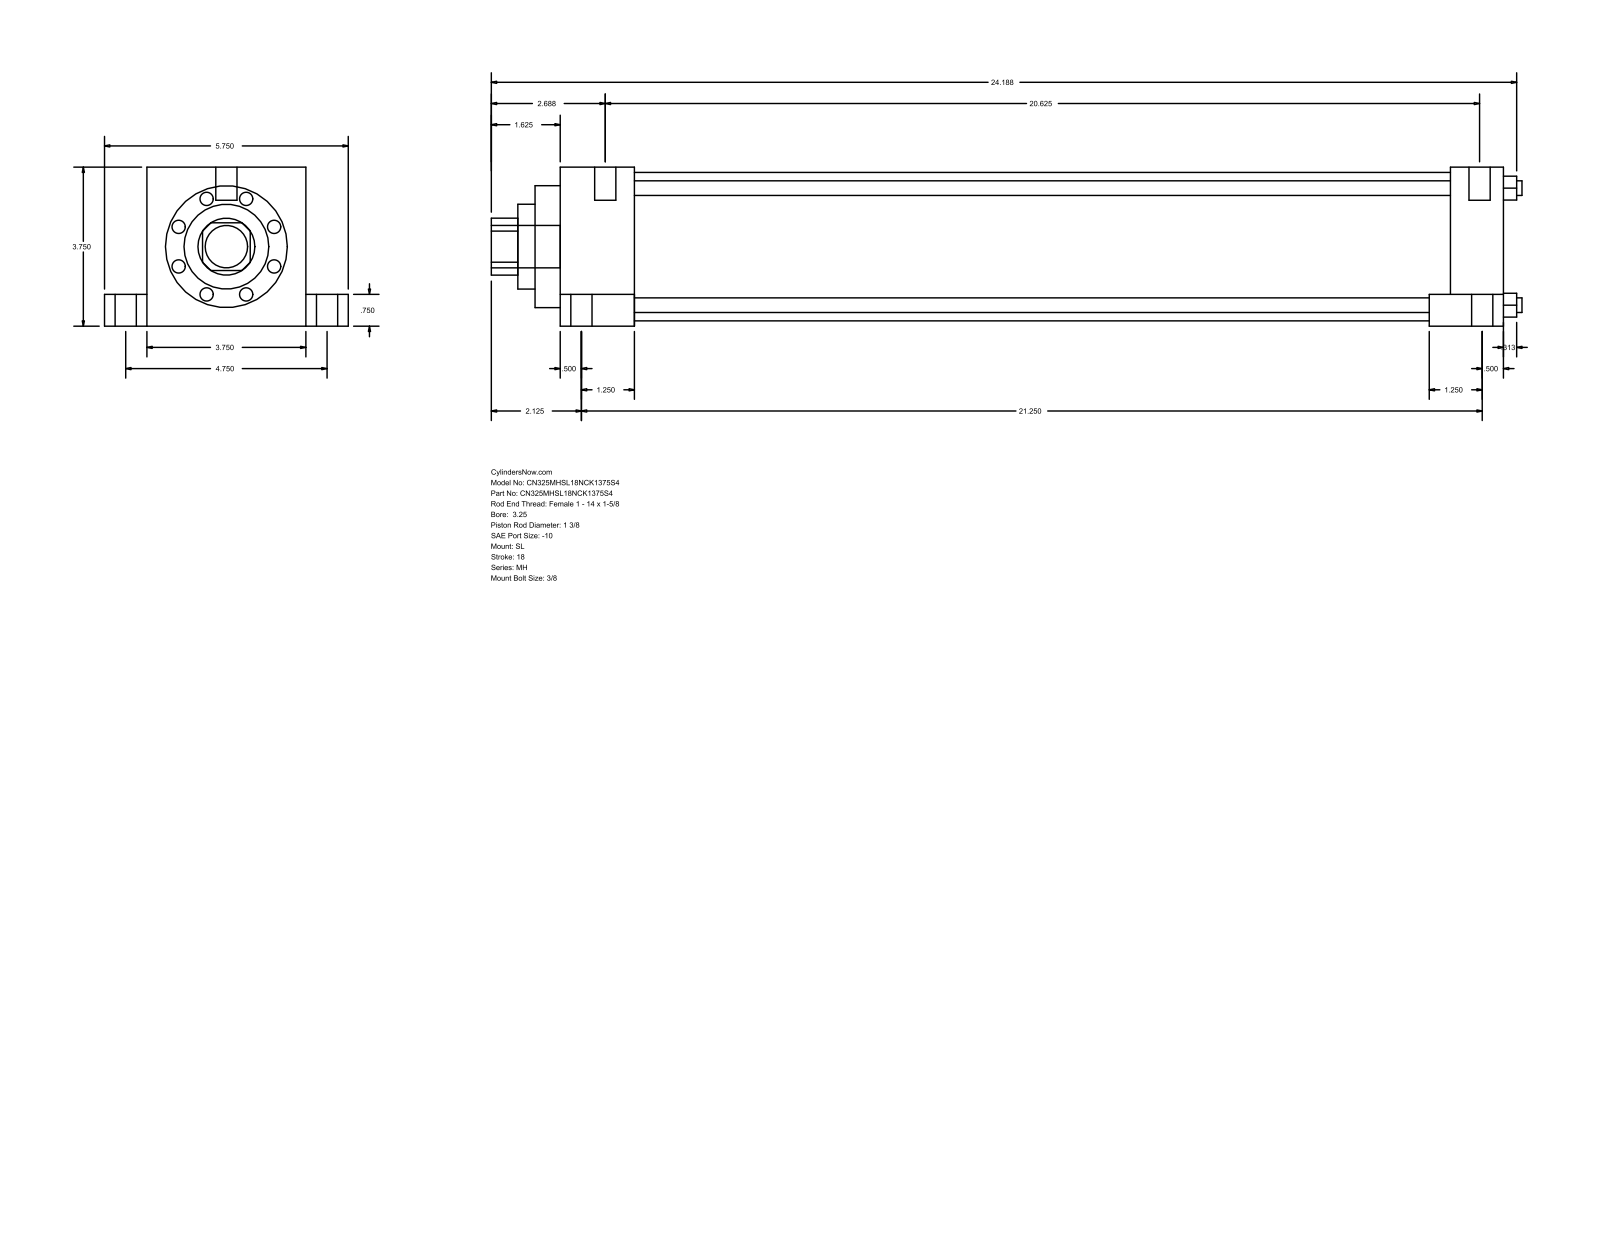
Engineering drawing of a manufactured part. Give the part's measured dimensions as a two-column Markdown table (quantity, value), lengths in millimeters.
| quantity | value |
| --- | --- |
| part name | MH_SL__0325_1.375 |
| STEP written by | GSSL Pune (CONFIG_CONTROL_DESIGN) |
| units | millimeters |
| bodies | 0 solids, 110 faces (77 planar, 33 cylindrical, 0 other) |
| overall size | 617.54 × 146.05 × 95.25 |
| round holes (diameter × count) | 8.76 × 4, 34.92 × 1, 50.8 × 1, 73.03 × 1, 88.9 × 1 |
| round bosses / shafts (diameter × count) | 12.7 × 6, 19.05 × 4, 5.56 × 4, 25.4 × 1 |
| partial cylindrical surfaces (radius × count) | 17.06 × 1 |
| main face-to-face distances | 95.24, 565.15, 44.45, 520.7, 25.41, 120.65, 19.05, 76.19, 533.4, 488.95 |
| hole center spacings | 49.57, 70.1, 99.14 |
